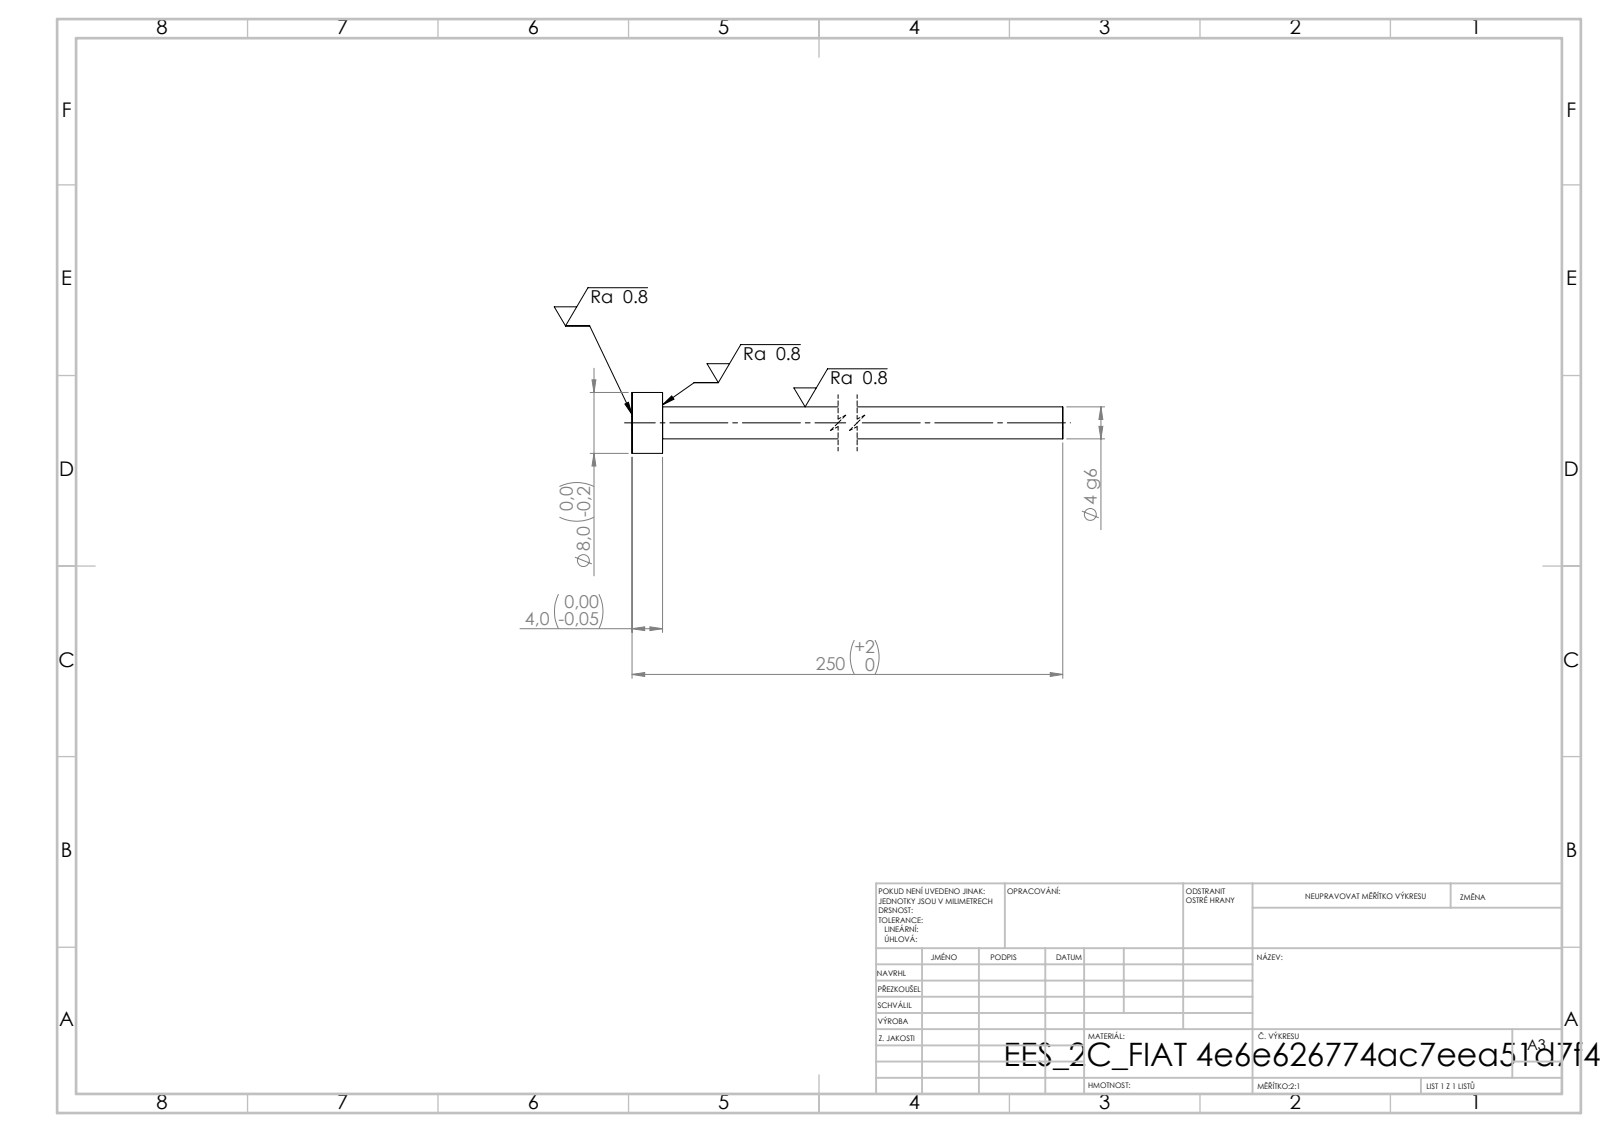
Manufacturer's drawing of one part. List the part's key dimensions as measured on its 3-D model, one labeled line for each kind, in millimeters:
STEP written by: SolidWorks 2019 (CONFIG_CONTROL_DESIGN)
Units: millimetres
Bodies: 1 solid, 7 faces (3 planar, 4 cylindrical, 0 other)
Overall size (bounding box): 250 × 8 × 8
Volume: 3 609 mm³ · Surface area: 3 447 mm²
Round bosses / shafts (diameter × count): ⌀8 ×1, ⌀4.2 ×1
Main face-to-face distances: 4, 250, 246
